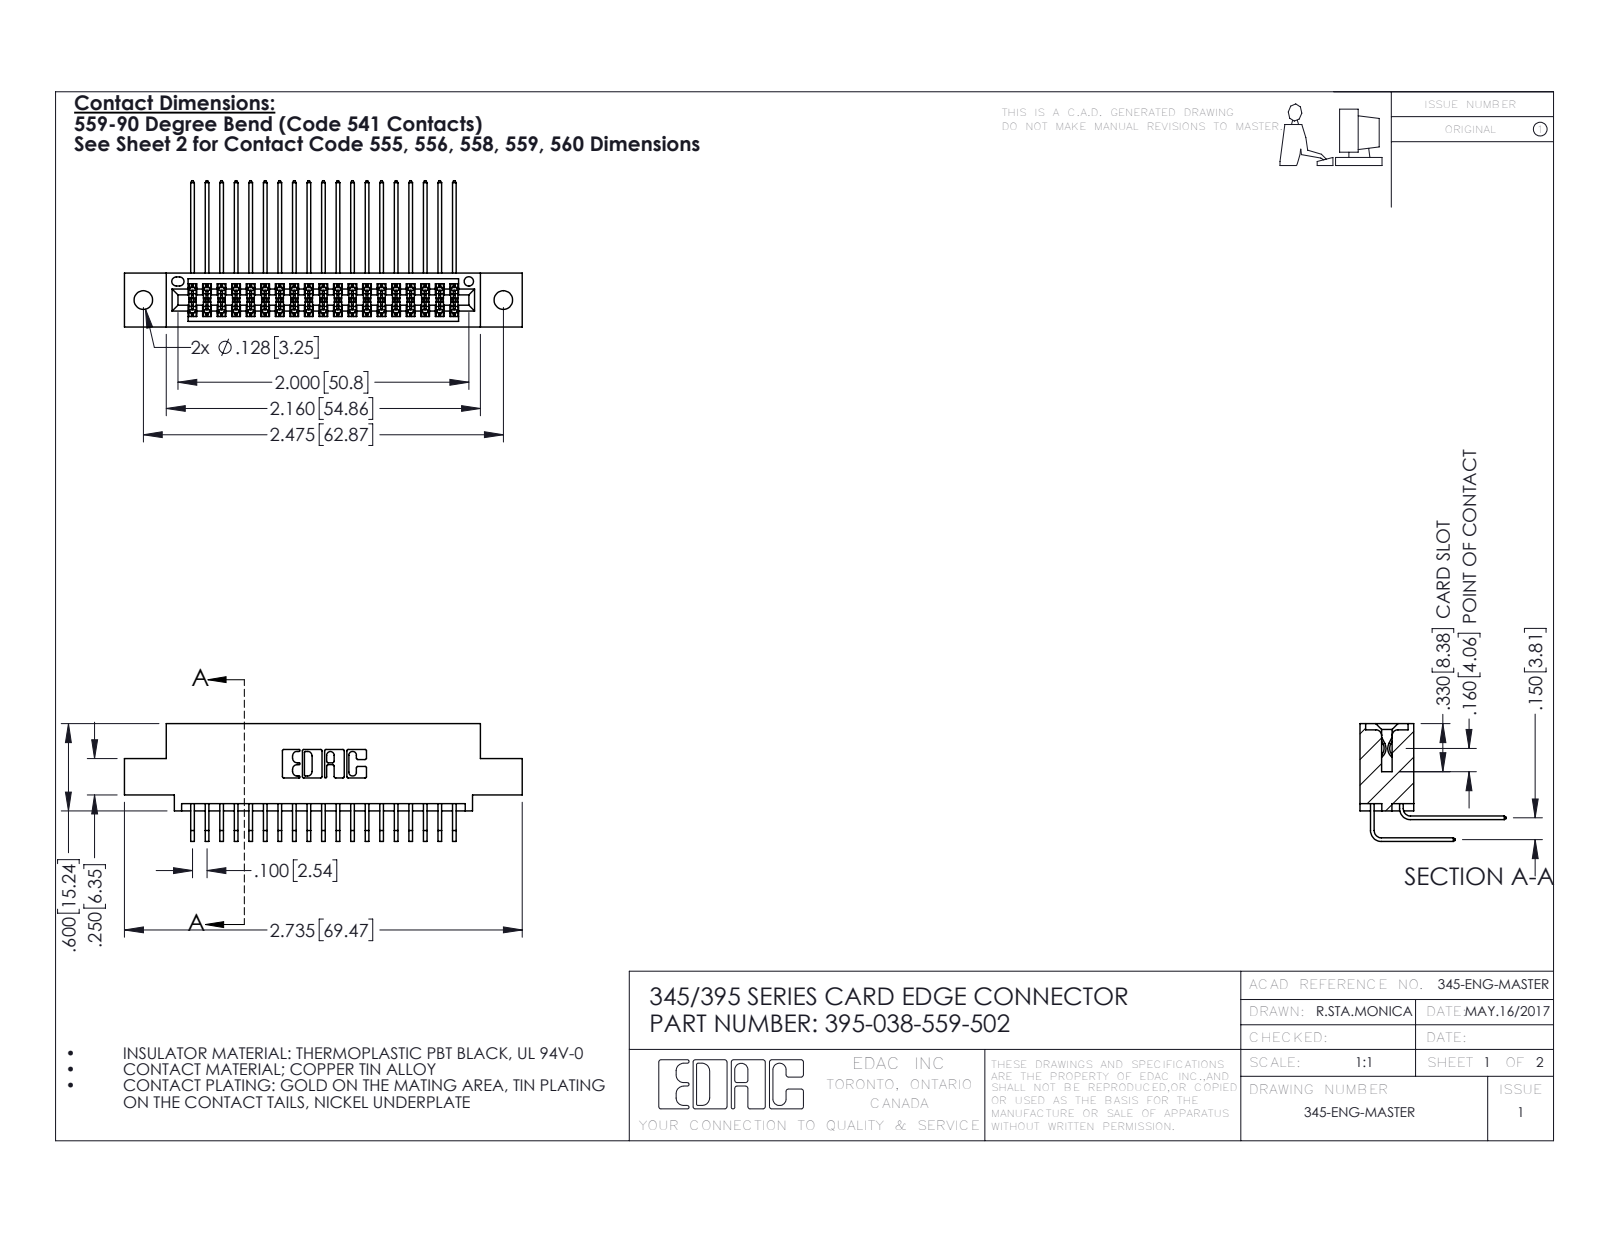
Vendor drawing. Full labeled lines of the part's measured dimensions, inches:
Part name (STEP PRODUCT): 345 Part_0.110 Offset - 0.128 Dia; 345-292-001_559 Tail - 2; 395-038-559-502; 345-292-001_558 559 Tail - 1
STEP written by: SolidWorks 2016 (CONFIG_CONTROL_DESIGN)
Units: inches
Bodies: 39 solids, 2106 faces (1414 planar, 692 cylindrical, 0 other)
Overall size (bounding box): 2.735 × 1.005 × 0.809
Volume: 0.405 in³ · Surface area: 15.85 in²
Round holes (diameter × count): ⌀0.128 ×2, ⌀0.064 ×1
Partial cylindrical surfaces — rounded edges, fillets, slot ends (radius × count): R0.006 ×58, R0.01 ×22, R0.007 ×6, R0.031 ×6, R0.026 ×3, R0.014 ×2, R0.019 ×2, R0.022 ×2
Main face-to-face distances: 0.072, 0.298, 0.2, 0.37, 0.098, 0.272, 0.025, 0.225, 0.15, 0.175
Hole centre spacings: 0.27, 2.241, 2.475
